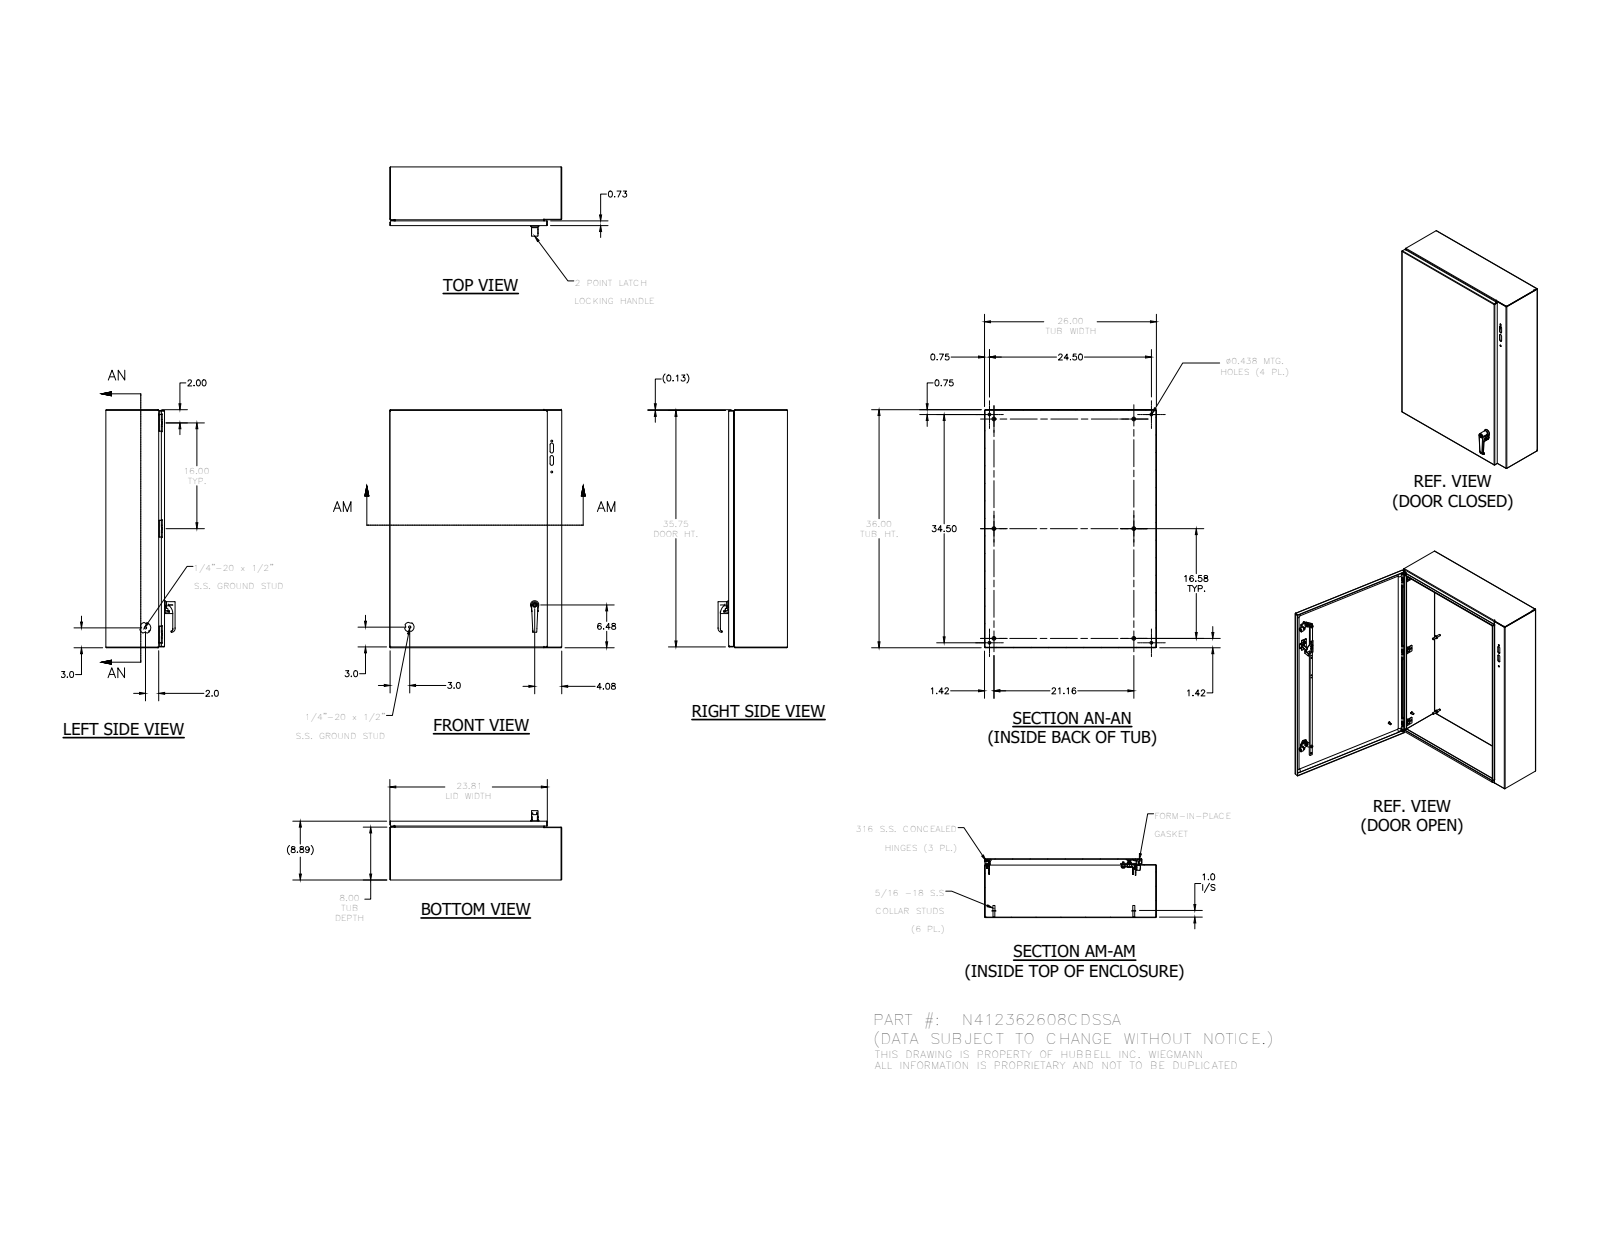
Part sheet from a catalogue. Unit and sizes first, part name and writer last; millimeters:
Units: millimetres
Overall size (bounding box): 914.4 × 660.4 × 266.2
Round holes (diameter × count): ⌀2.4 ×6, ⌀3.7 ×6, ⌀3.9 ×6, ⌀4.2 ×6, ⌀4.4 ×6, ⌀4.7 ×6, ⌀4 ×5, ⌀11.1 ×4, ⌀8.1 ×3, ⌀5 ×2, ⌀5.4 ×2, ⌀5.6 ×2
Round bosses / shafts (diameter × count): ⌀6.4 ×16, ⌀7.6 ×10, ⌀14.3 ×6, ⌀9.1 ×6, ⌀8.1 ×6, ⌀6.5 ×6, ⌀4.2 ×6, ⌀3.3 ×6
Partial cylindrical surfaces — rounded edges, fillets, slot ends (radius × count): R0.5 ×38, R1.3 ×38, R3.2 ×33, R0.3 ×30, R0.8 ×30, R0.4 ×26, R0.6 ×16, R2.7 ×16
Main face-to-face distances: 1.9, 223.8, 221.9, 225.7, 912.5, 1.9, 658.5, 656.6, 658.5, 660.4
Hole centre spacings: 406.4, 12.7, 812.8, 406.6, 16.7, 16.8, 33.2, 33.3
Volume: 4 202 000 mm³ · Surface area: 4 217 000 mm²
Bodies: 72 solids, 2526 faces (942 planar, 918 cylindrical, 666 other)
Part name (STEP PRODUCT): N412362608CDSSA
STEP written by: SolidWorks 2019 (AUTOMOTIVE_DESIGN)
